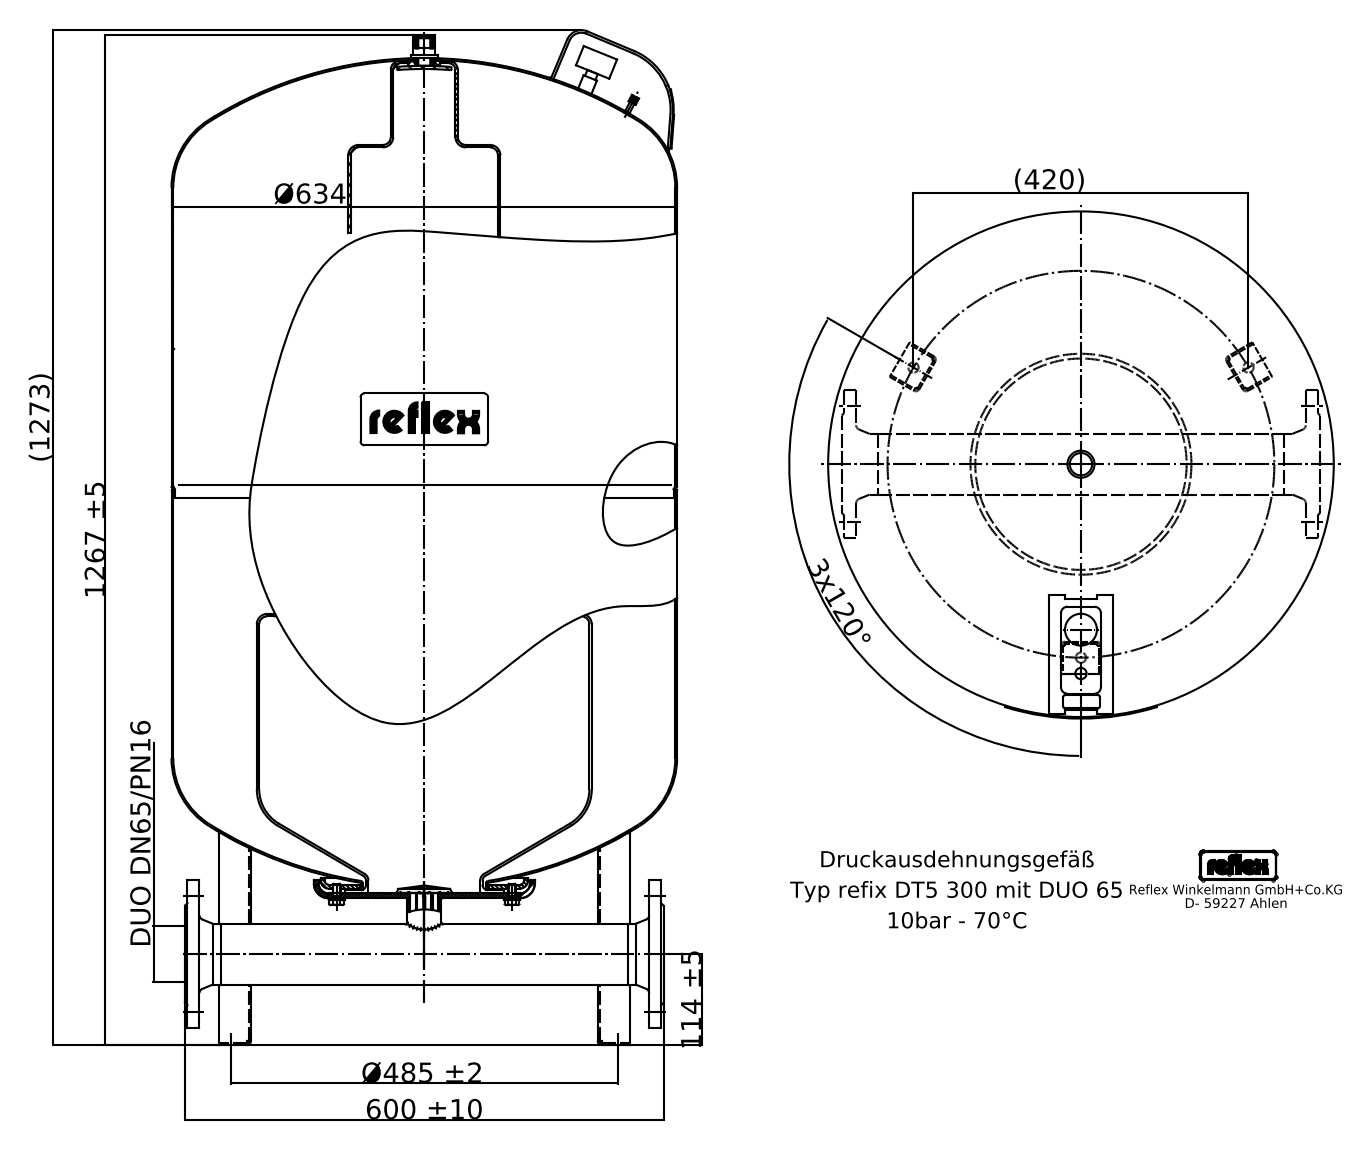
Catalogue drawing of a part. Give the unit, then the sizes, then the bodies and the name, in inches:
Units: inches
Overall size (bounding box): 49.937 × 24.961 × 24.961
Round holes (diameter × count): ⌀0.748 ×4, ⌀0.528 ×3, ⌀0.098 ×1, ⌀0.15 ×1, ⌀0.169 ×1, ⌀0.173 ×1, ⌀0.215 ×1, ⌀0.276 ×1, ⌀0.315 ×1, ⌀0.449 ×1, ⌀2.996 ×1, ⌀6.181 ×1
Round bosses / shafts (diameter × count): ⌀0.394 ×9, ⌀24.961 ×1, ⌀10.236 ×1, ⌀9.055 ×1, ⌀7.283 ×1, ⌀2.441 ×1, ⌀1.669 ×1, ⌀1.339 ×1
Partial cylindrical surfaces — rounded edges, fillets, slot ends (radius × count): R0.039 ×15, R0.098 ×15, R0.197 ×15, R0.221 ×4, R0.089 ×3, R0.151 ×2, R0.266 ×2, R0.315 ×2
Main face-to-face distances: 28.189, 0.098, 1.87, 6.693, 34.882, 0.236, 6.929, 35.118, 0.197, 1.969
Hole centre spacings: 2.855, 4.037, 9.547, 16.536, 5.709
Volume: 18 160 in³ · Surface area: 6 735 in²
Bodies: 23 solids, 521 faces (223 planar, 185 cylindrical, 113 other)
STEP written by: Mechanical Desktop 2008 (CONFIG_CONTROL_DESIGN)
